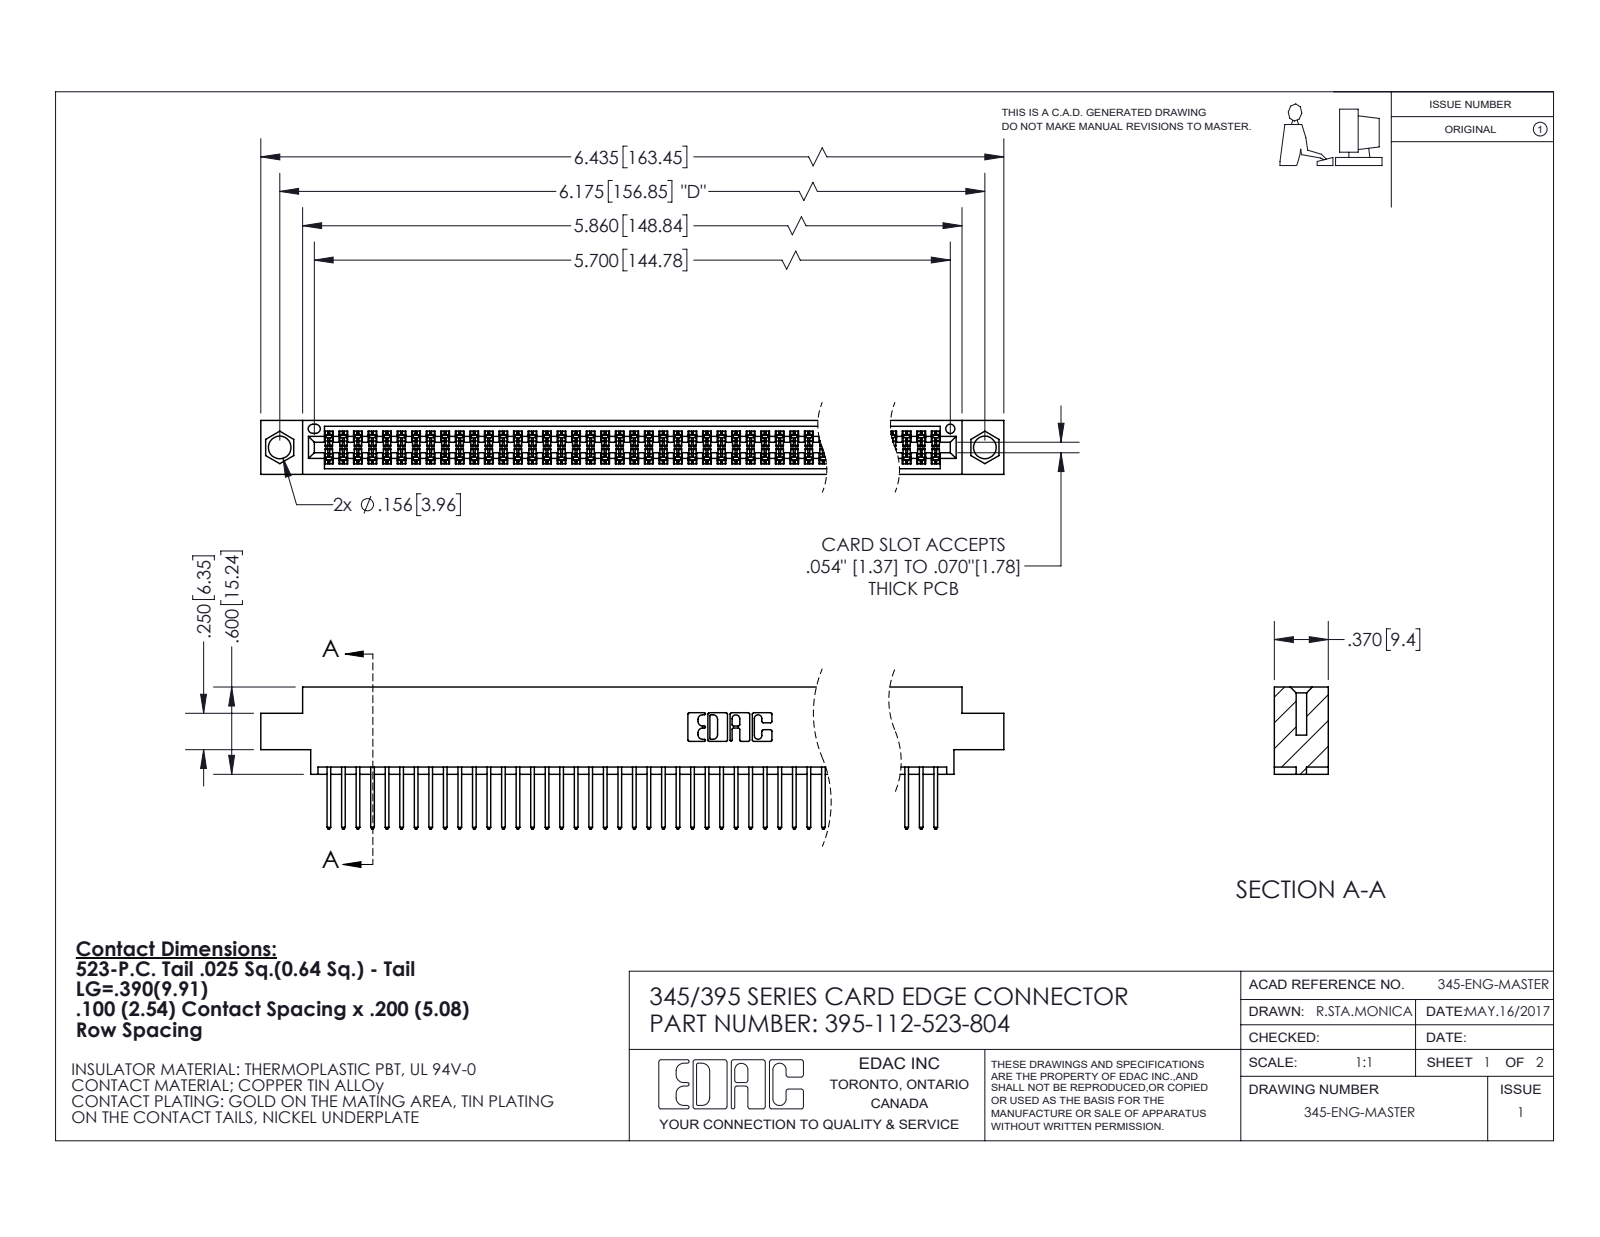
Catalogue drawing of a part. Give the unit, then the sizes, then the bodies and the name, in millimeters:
Units: millimetres
Overall size (bounding box): 163.4 × 24.8 × 9.4
Round holes (diameter × count): ⌀4 ×2, ⌀1.6 ×1
Partial cylindrical surfaces — rounded edges, fillets, slot ends (radius × count): R0.2 ×224, R0.3 ×112, R0.3 ×22, R0.2 ×6, R0.8 ×6, R0.7 ×3, R0.4 ×2, R0.5 ×2
Main face-to-face distances: 1.8, 7.6, 5.1, 2.5, 6.9, 0.6, 9.4, 5.7, 4.4, 3.8
Hole centre spacings: 6.9, 150.9, 156.8
Volume: 16 000 mm³ · Surface area: 24 970 mm²
Bodies: 113 solids, 5744 faces (3794 planar, 1950 cylindrical, 0 other)
Part name (STEP PRODUCT): 345-292-001_345-293-123; 345 Part_0.170 Offset - 0.156 Dia-TI; 395-112-523-804
STEP written by: SolidWorks 2020 (CONFIG_CONTROL_DESIGN)
